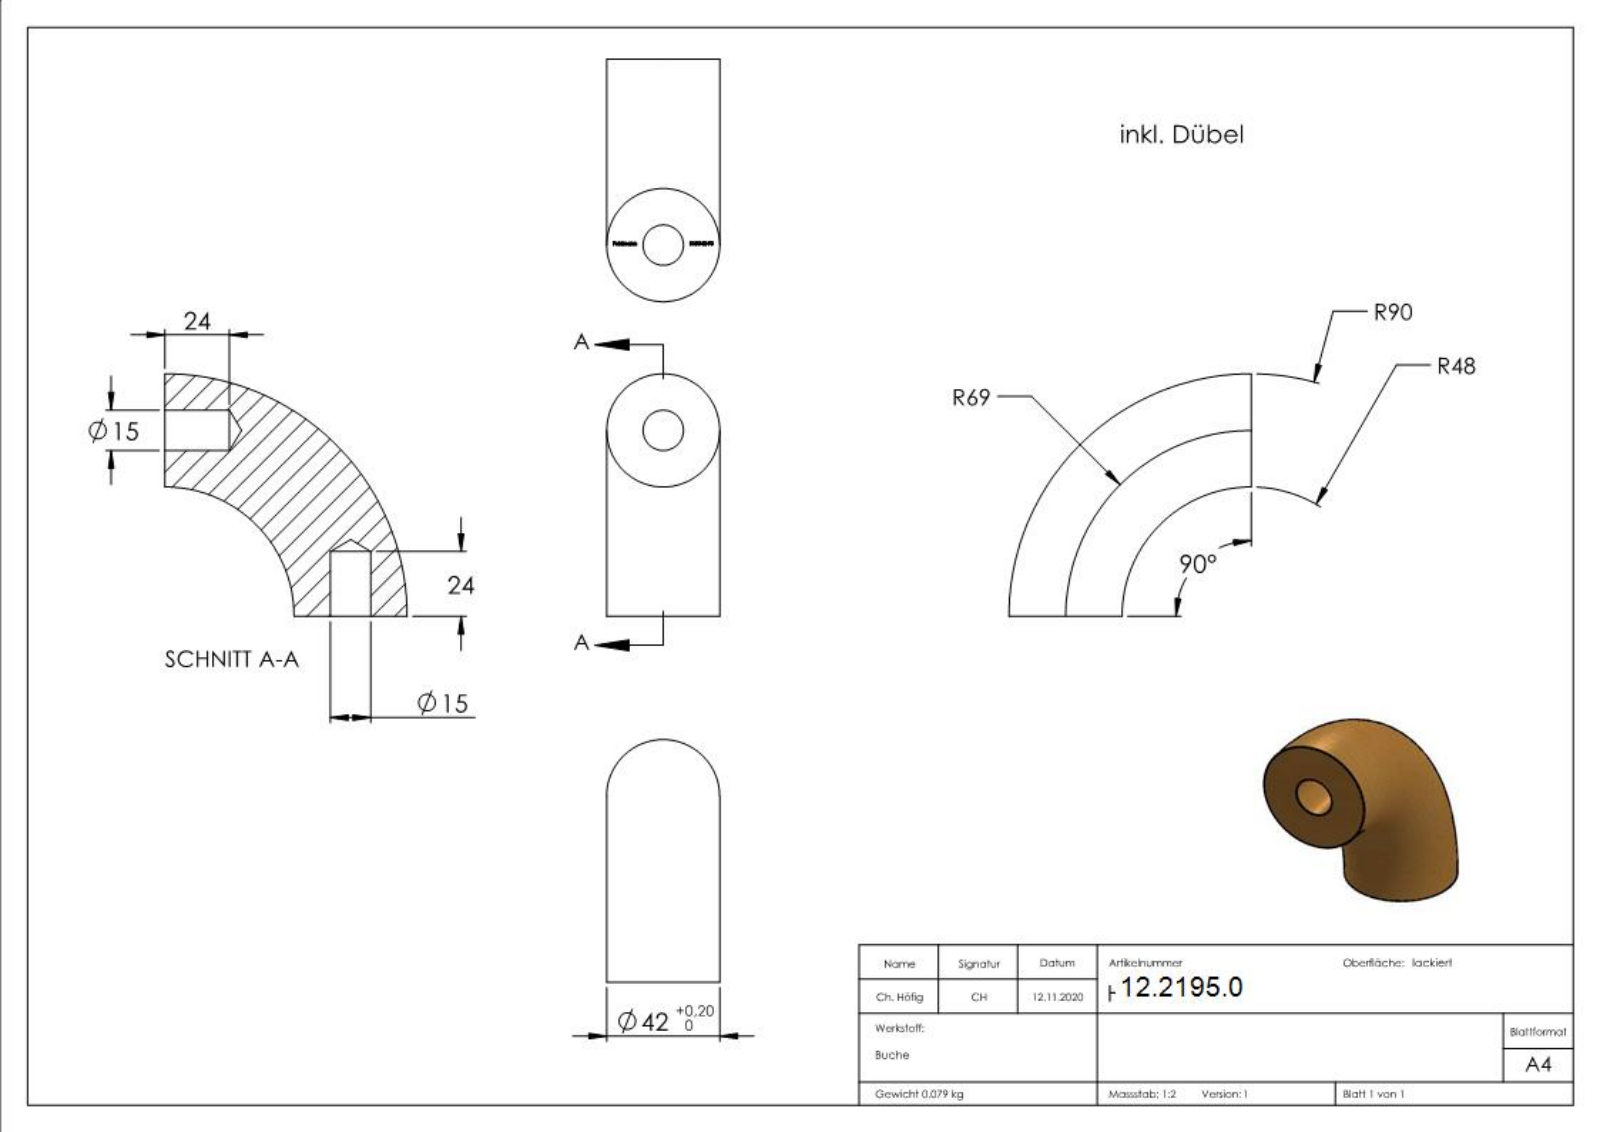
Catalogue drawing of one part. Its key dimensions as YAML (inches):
part_name: "H-BU42-90"
step_written_by: "SolidWorks 2018 (CONFIG_CONTROL_DESIGN)"
units: inches
bodies: {solids: 1, faces: 236, planar: 138, cylindrical: 4, other: 94}
overall_size: [3.543, 3.543, 1.654]
volume: 8.613
surface_area: 30.07
round_holes:
  - {diameter: 0.591, count: 2}
face_to_face_distances: [0.181, 2.717, 0.117, 0.041, 0.017, 1.124, 0.031, 1.198, 0.073, 1.156]
